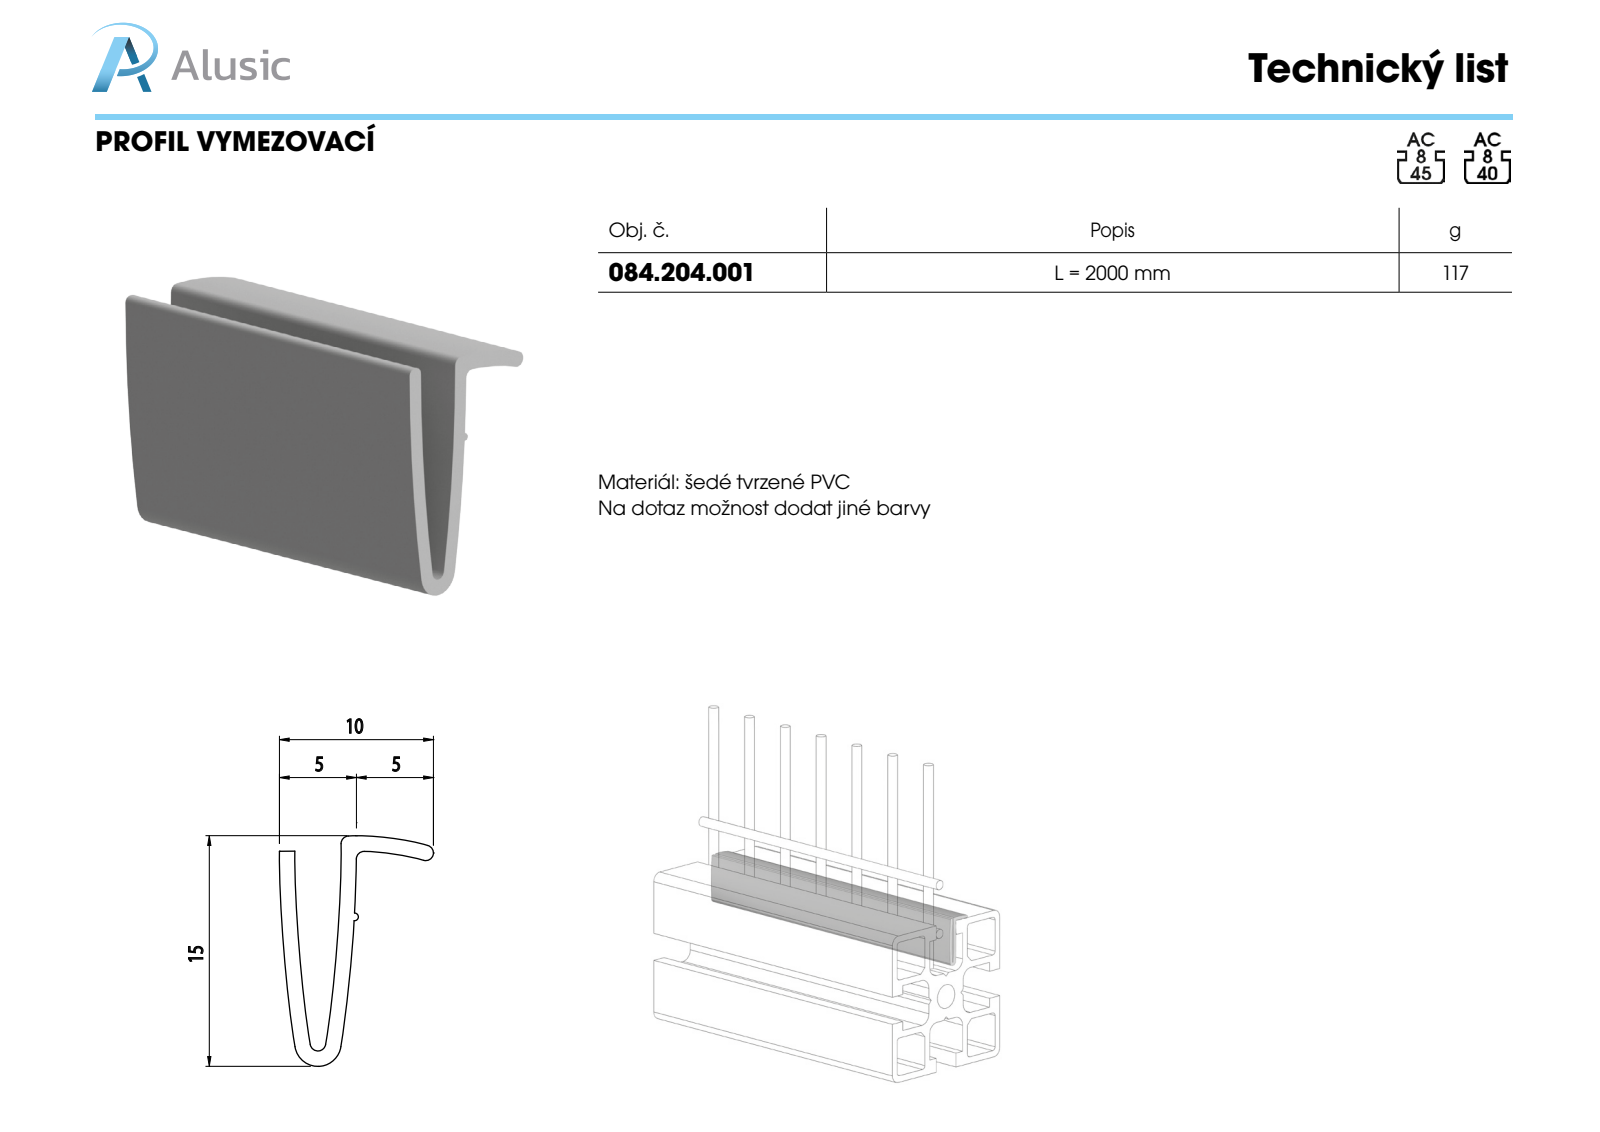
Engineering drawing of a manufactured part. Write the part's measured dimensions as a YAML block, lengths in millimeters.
part_name: "084.204.001"
step_written_by: "SolidWorks 2011 (CONFIG_CONTROL_DESIGN)"
units: millimeters
bodies: {solids: 1, faces: 20, planar: 3, cylindrical: 17, other: 0}
overall_size: [100, 15, 10]
volume: 3523
surface_area: 7234
partial_cylinders:
  - {radius: 0.5, count: 3}
  - {radius: 0.4, count: 2}
  - {radius: 88.62, count: 2}
  - {radius: 89.62, count: 2}
  - {radius: 0.25, count: 1}
  - {radius: 0.5, count: 1}
  - {radius: 1.5, count: 1}
  - {radius: 16.5, count: 1}
face_to_face_distances: [100]
